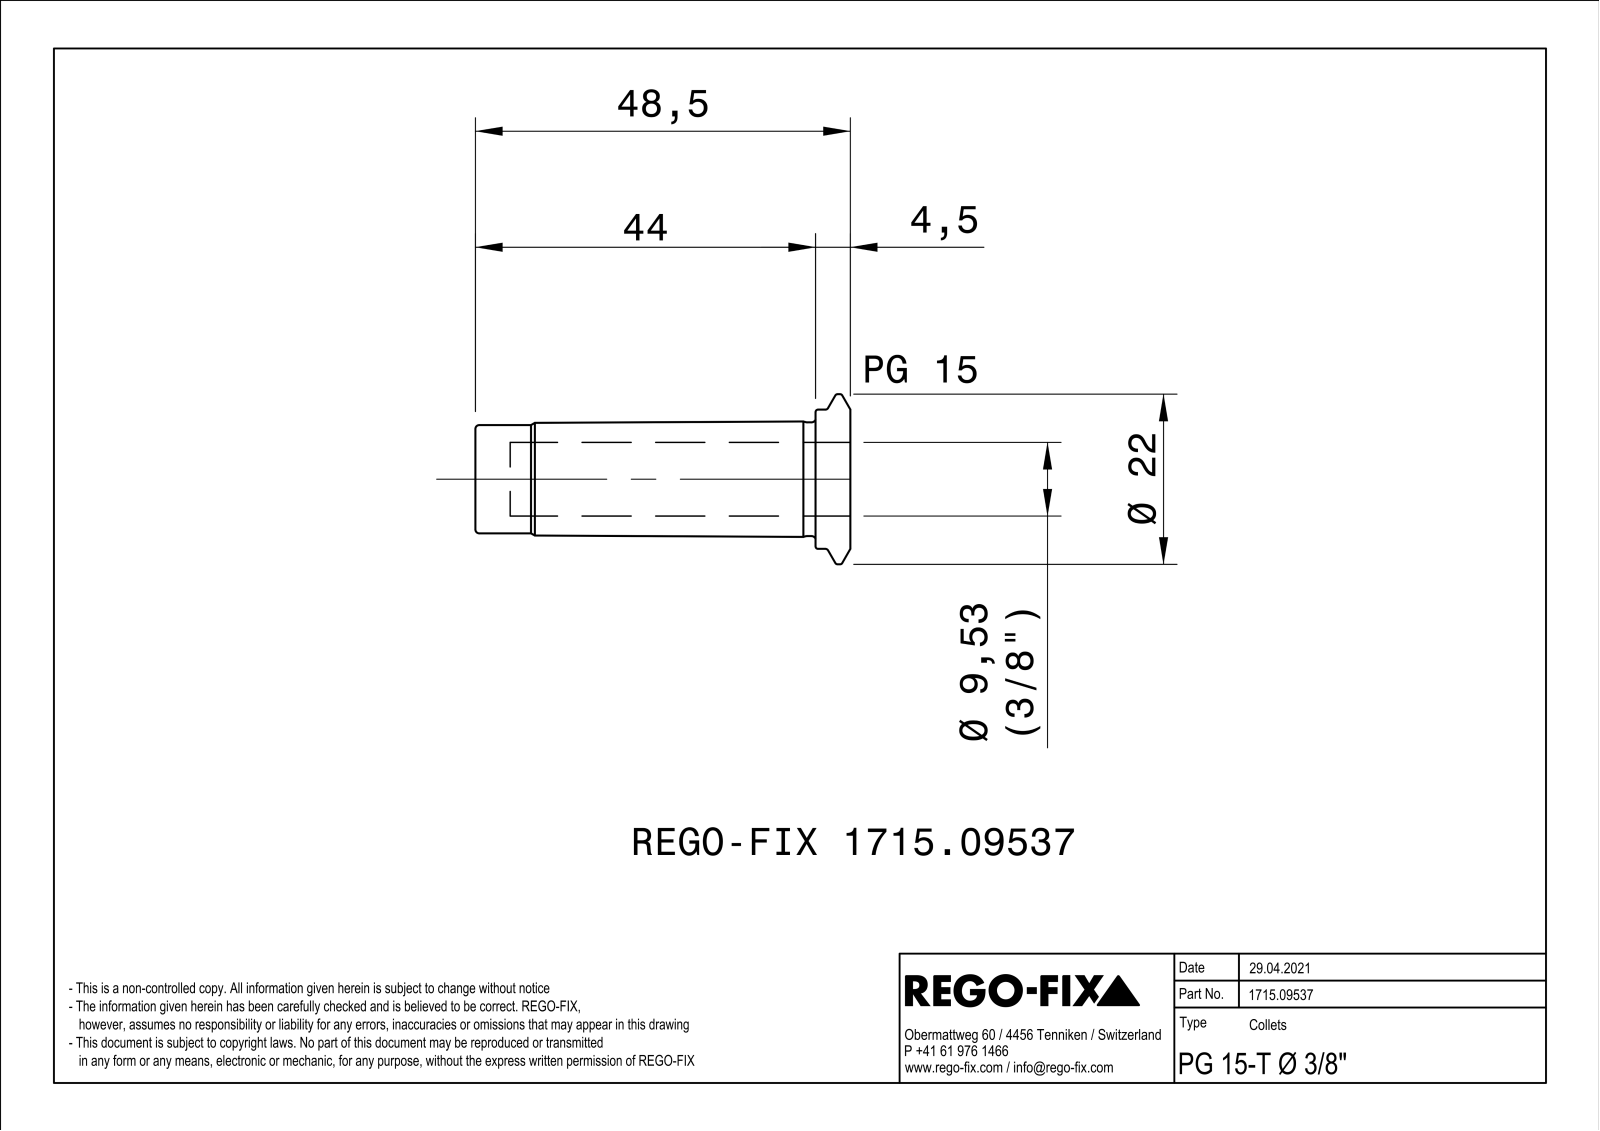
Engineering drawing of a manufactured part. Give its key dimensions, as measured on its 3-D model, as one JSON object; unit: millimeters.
{"part_name": "NOCUT", "step_written_by": "SIEMENS PLM Software Solid Edge ST10 (AUTOMOTIVE_DESIGN)", "units": "millimeters", "bodies": {"solids": 1, "faces": 82, "planar": 14, "cylindrical": 27, "other": 41}, "overall_size": [48.5, 22, 21.85], "volume_mm3": 4777, "surface_area_mm2": 4663, "round_holes": [[2.46, 1], [9.53, 1], [11, 1], [11.4, 1]], "round_bosses_or_shafts": [[22, 1], [18, 1], [14.7, 1], [14, 1]], "partial_cylinders_radius": [[0.5, 6], [1.65, 1], [2, 1], [2.95, 1], [3.01, 1]], "face_to_face_distances": [1, 48.5, 4.5, 44, 47.9, 43.4, 0.6, 46.8, 42.3, 1.1]}
